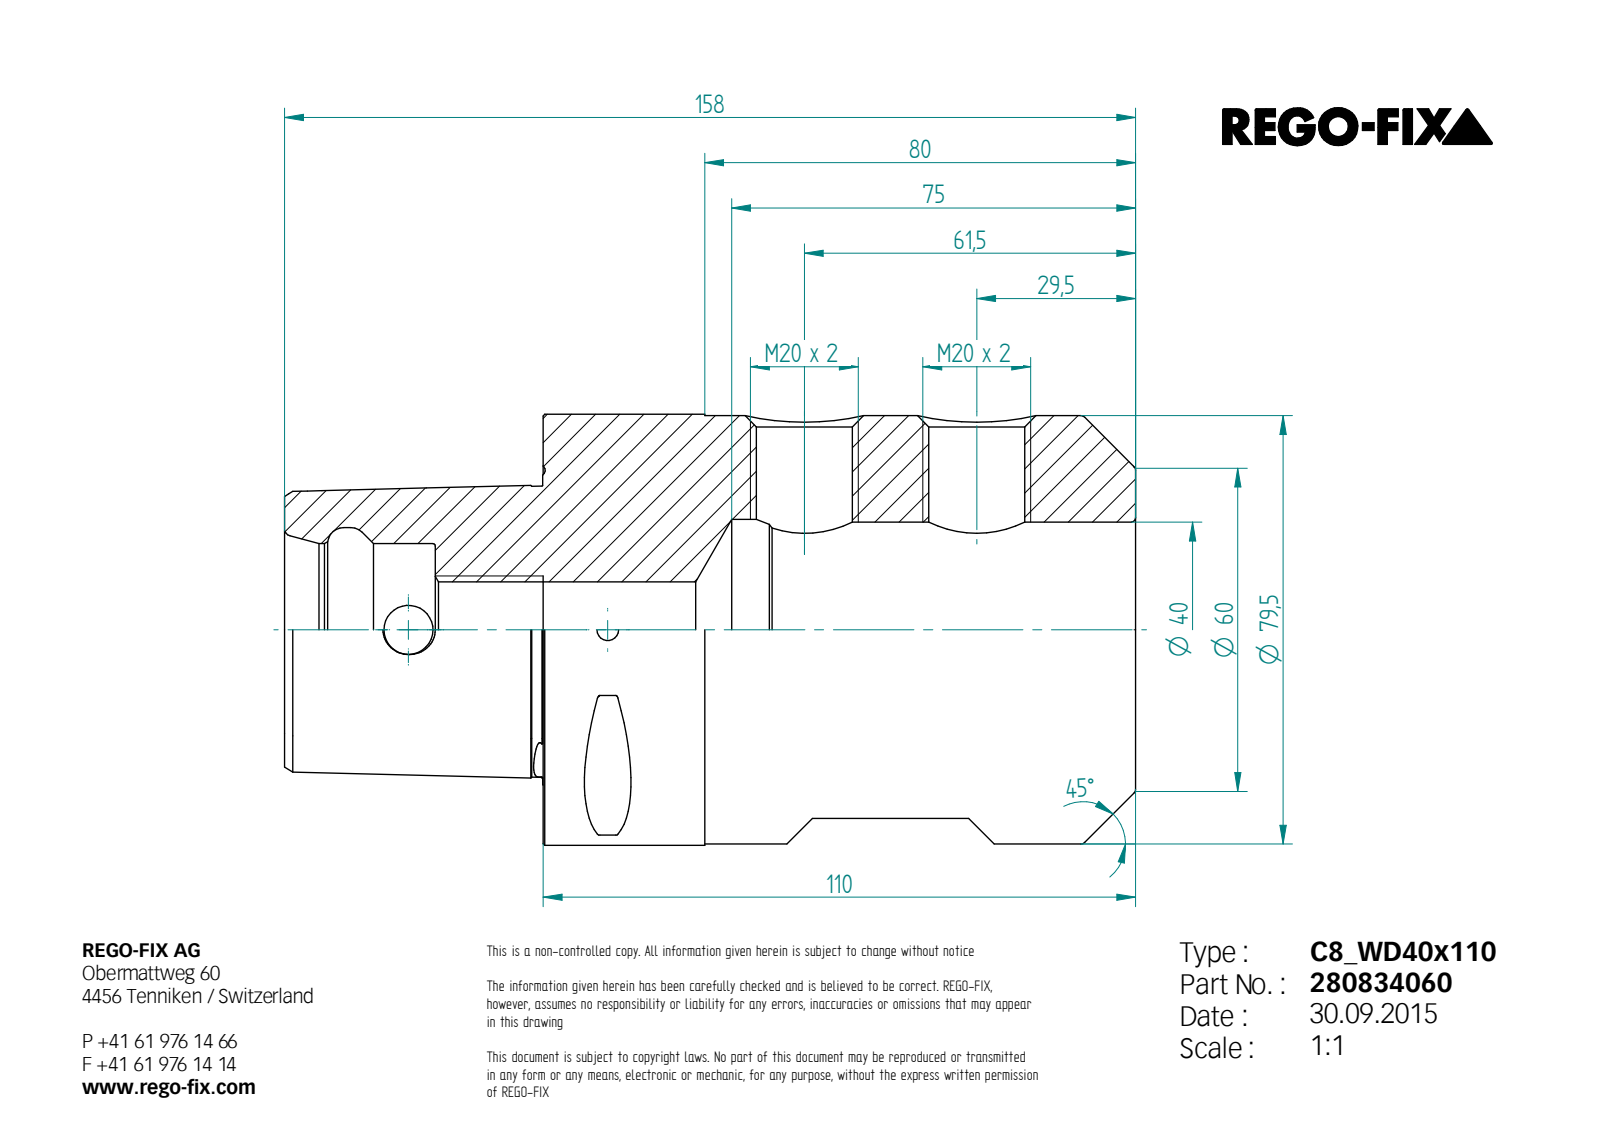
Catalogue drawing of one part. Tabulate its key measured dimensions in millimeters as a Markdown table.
| quantity | value |
| --- | --- |
| STEP written by | Unknown (AUTOMOTIVE_DESIGN) |
| units | millimeters |
| bodies | 1 solid, 104 faces (23 planar, 22 cylindrical, 59 other) |
| overall size | 158 × 80 × 80 |
| volume | 489 356 mm³ |
| surface area | 60 781 mm² |
| round holes (diameter × count) | 17.84 × 3, 4 × 1, 9.1 × 1, 32 × 1, 38 × 1, 40 × 1, 41 × 1 |
| round bosses / shafts (diameter × count) | 80 × 1, 79.5 × 1 |
| partial cylindrical surfaces (radius × count) | 0.5 × 8 |
| main face-to-face distances | 110, 48, 158, 32.55, 28, 20, 130, 47.9, 19.9, 110.1 |
| hole center spacings | 32, 37 |
